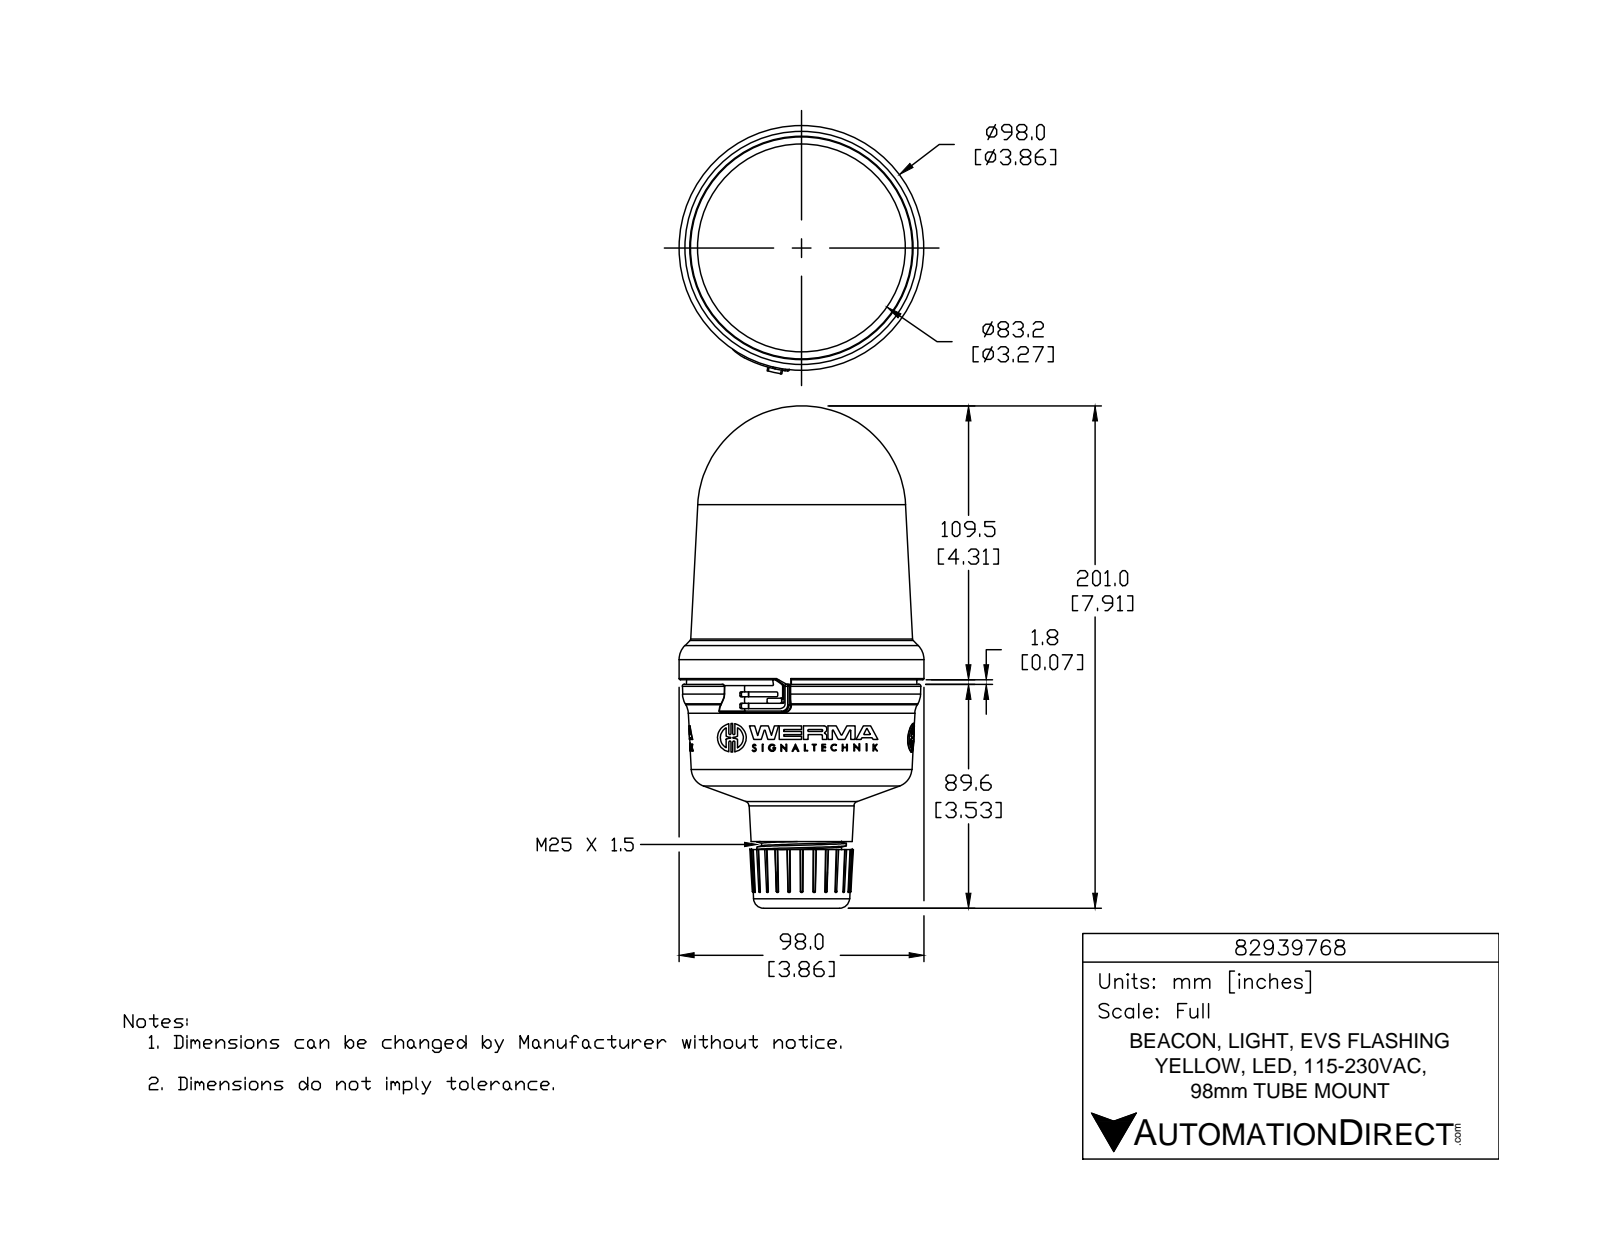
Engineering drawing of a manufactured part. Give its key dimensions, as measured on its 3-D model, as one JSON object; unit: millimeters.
{"part_name": "82939768", "step_written_by": "SolidWorks 2015 (AUTOMOTIVE_DESIGN)", "units": "millimeters", "bodies": {"solids": 1, "faces": 1006, "planar": 554, "cylindrical": 189, "other": 263}, "overall_size": [201, 99.4, 98], "volume_mm3": 896400, "surface_area_mm2": 58960, "round_holes": [[2, 3], [25.7, 1], [26, 1]], "round_bosses_or_shafts": [[11.5, 3], [2.9, 3], [98, 1], [35.8, 1], [32, 1]], "partial_cylinders_radius": [[0.5, 12], [0.2, 9], [0.2, 6], [0.4, 6], [0.4, 6], [0.4, 6], [6.7, 6], [0.2, 3]], "face_to_face_distances": [56.2, 11.7, 68, 8.5, 3.2, 64.7, 66.1, 62.9, 54.4, 1.9]}
